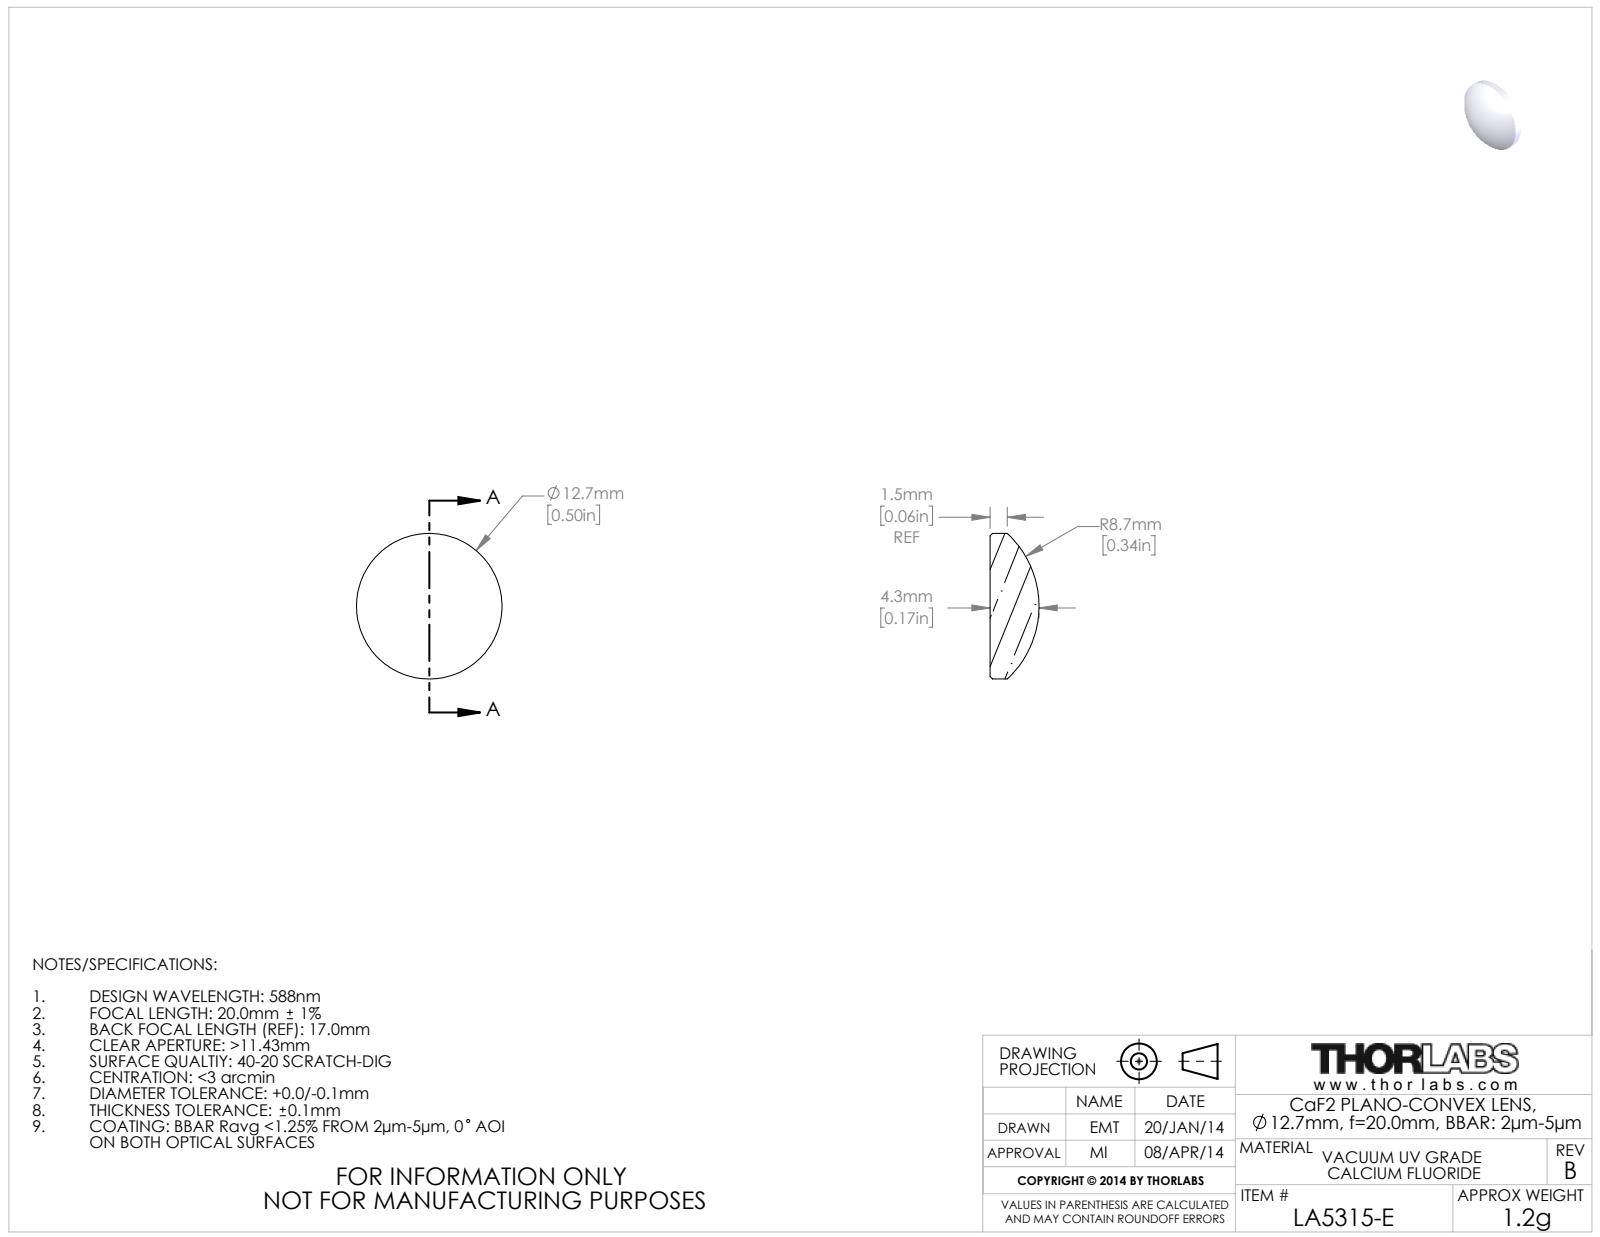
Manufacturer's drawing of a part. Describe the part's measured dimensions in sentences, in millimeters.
The part is named "20128-E0W". Its 3-D file was written by "SolidWorks 2018 (CONFIG_CONTROL_DESIGN)". It is 1 solid with 7 faces: 1 planar, 2 cylindrical and 4 other. Overall it measures 12.7 by 12.7 by 4.26 millimeters. Its volume is 375 cubic millimeters and its surface area 332 square millimeters. Round bosses or shafts: 1 of diameter 12.7.
